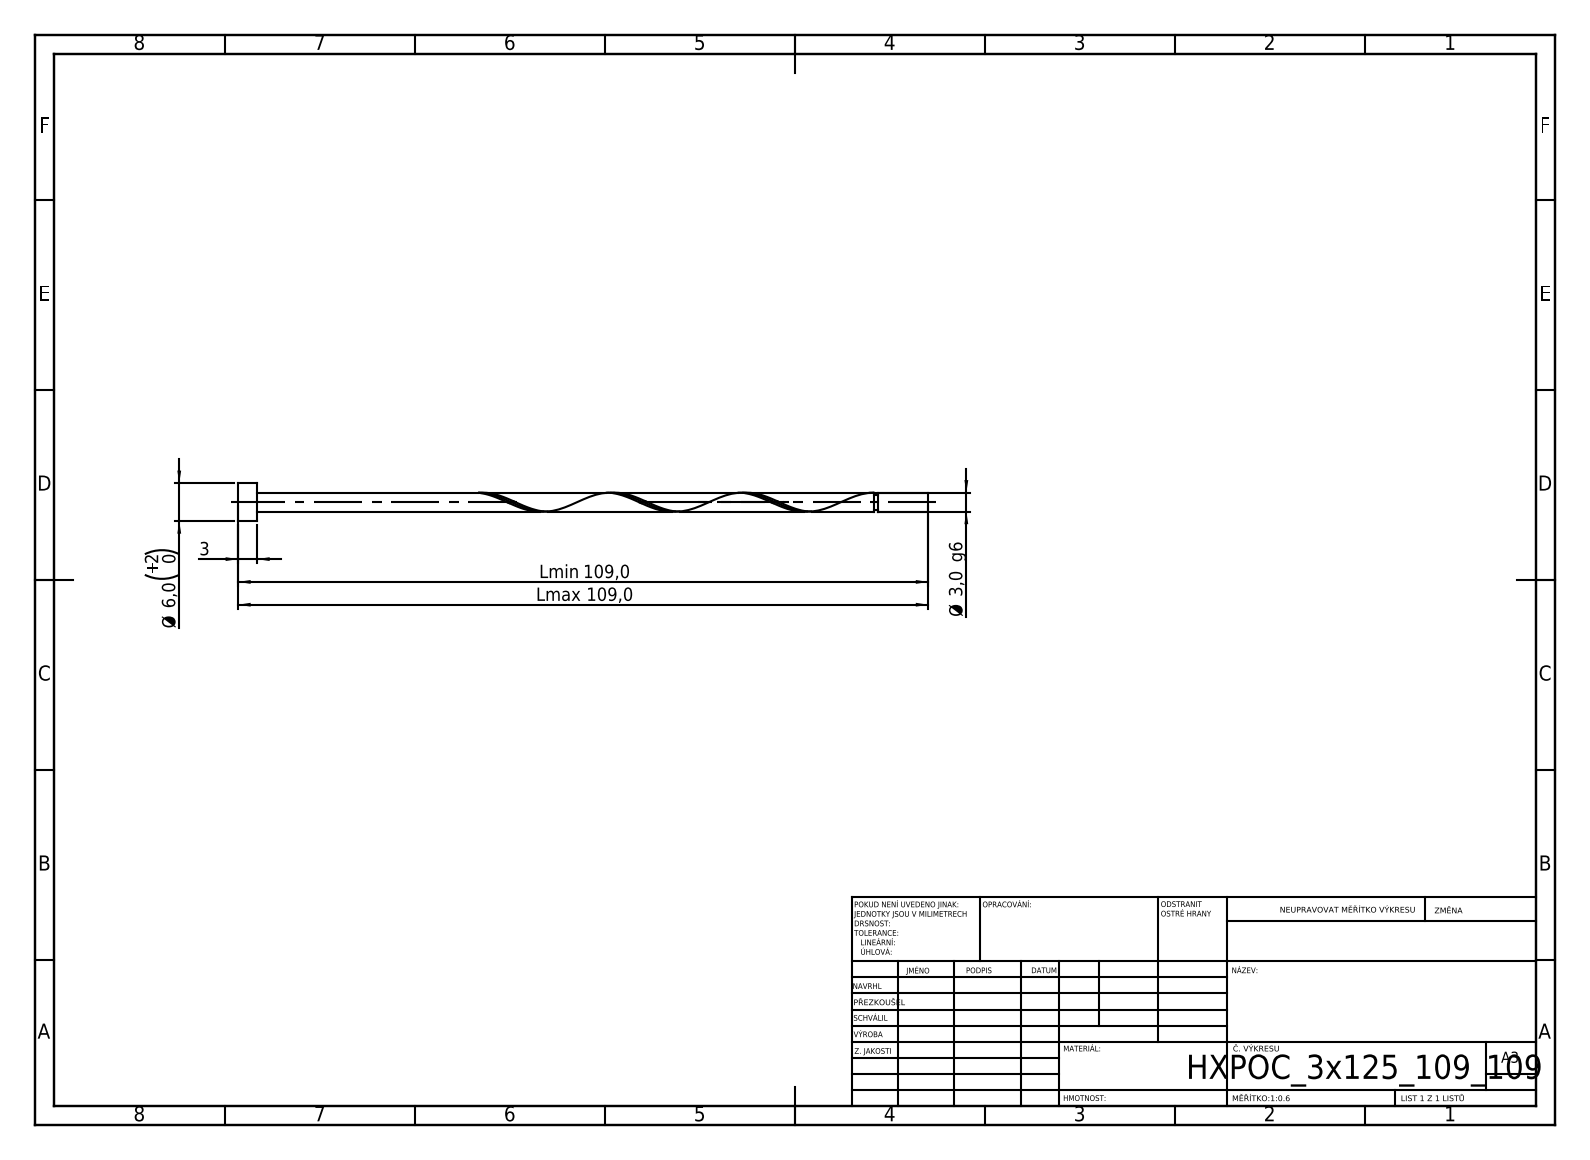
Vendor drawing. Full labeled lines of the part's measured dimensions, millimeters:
STEP written by: SolidWorks 2019 (CONFIG_CONTROL_DESIGN)
Units: millimetres
Bodies: 1 solid, 21 faces (6 planar, 14 cylindrical, 1 other)
Overall size (bounding box): 109 × 6 × 6
Volume: 824 mm³ · Surface area: 1 136 mm²
Round bosses / shafts (diameter × count): ⌀6 ×1, ⌀3 ×1, ⌀2.4 ×1
Main face-to-face distances: 3, 109, 106, 101.01, 98.01, 7.99, 100.41, 97.41, 0.6, 8.59
